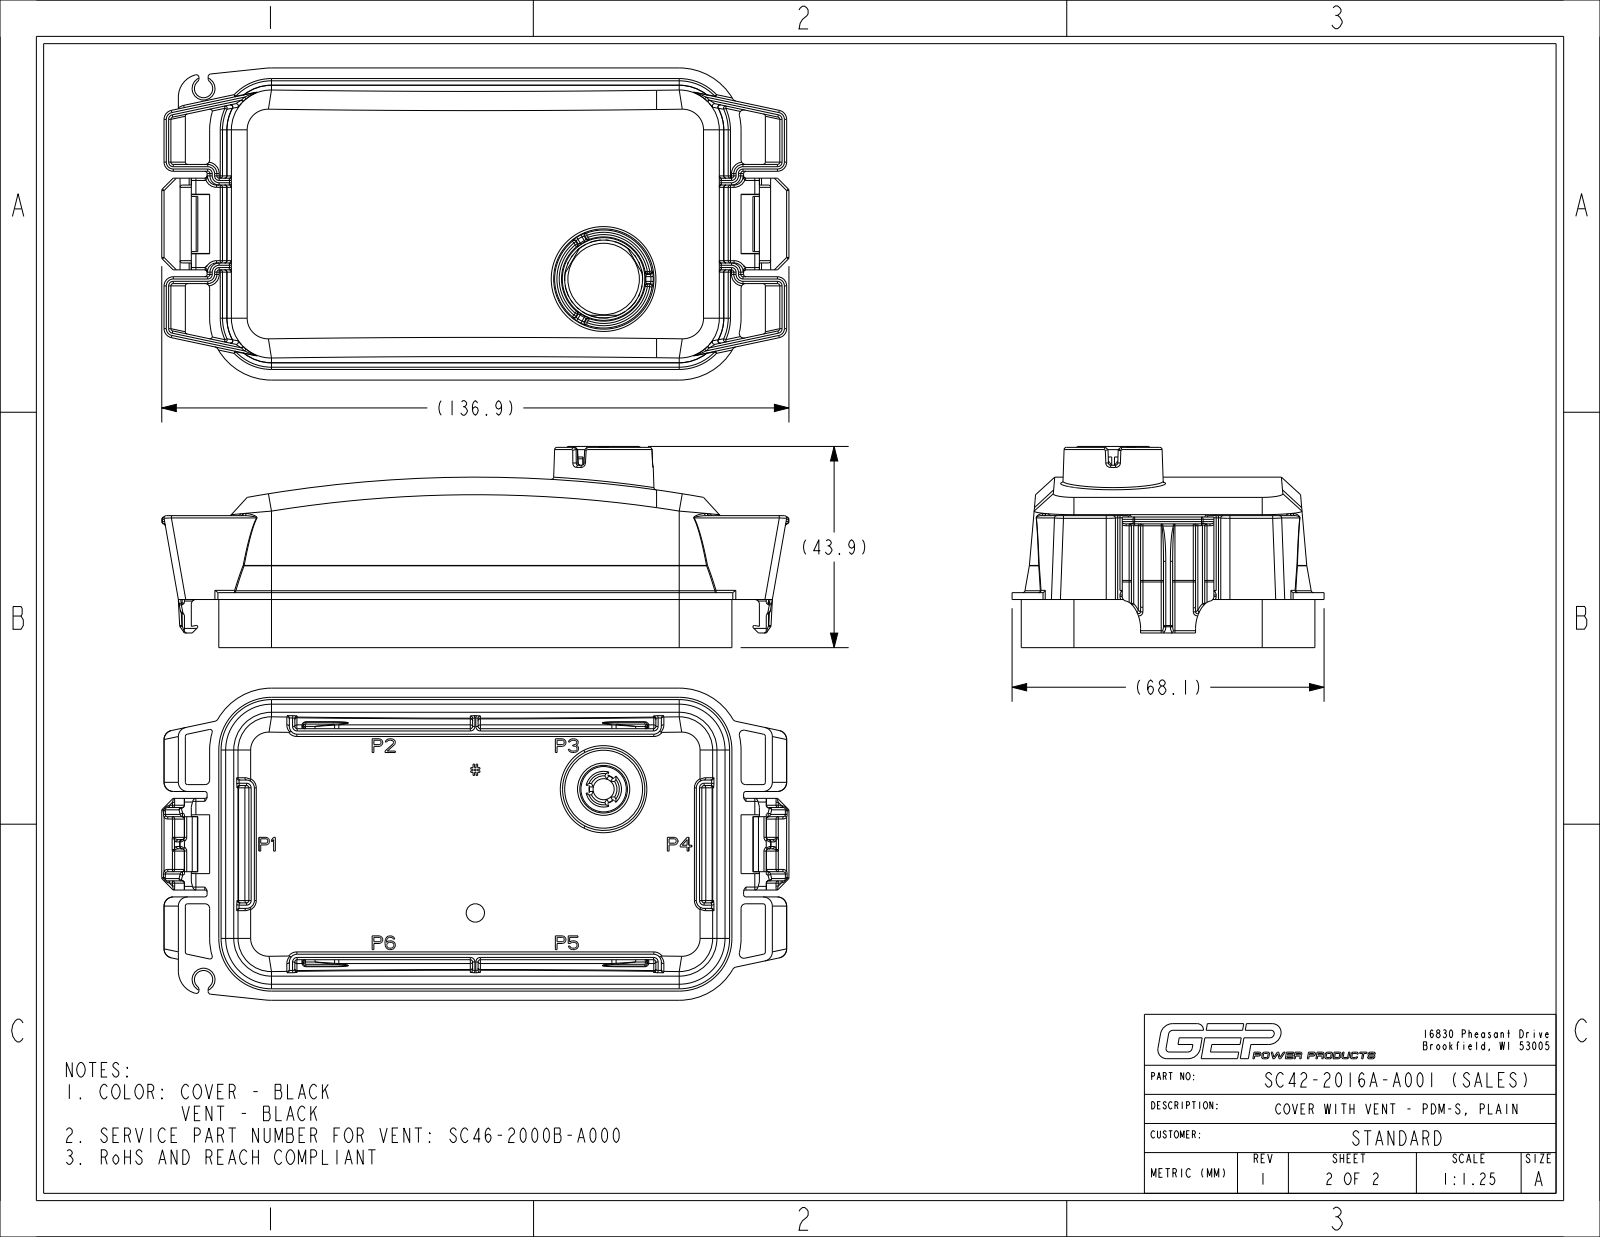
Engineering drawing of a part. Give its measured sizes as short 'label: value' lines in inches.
name: PC27-2000C-B001_NCF; PC46-2000B-A000_NCF; PC42-2016A-A001_NCF_ASM; SC42-2016A-A001_NCF_ASM
written by: CREO PARAMETRIC BY PTC INC, 2017110 (CONFIG_CONTROL_DESIGN)
unit: in
bodies: 3 solids, 1685 faces (467 planar, 452 cylindrical, 766 other)
size: 5.39 × 2.681 × 1.728
volume: 2.198 in³; area: 74.41 in²
holes: 1× ⌀0.157, 1× ⌀0.181, 1× ⌀0.252, 1× ⌀0.378
bosses: 1× ⌀0.669, 1× ⌀0.409, 1× ⌀0.244
rounds: 234× R0.02, 22× R0.079, 19× R0.039, 8× R0.067, 4× R0.016, 4× R0.02, 4× R0.024, 4× R0.394
face distances: 0.059, 2.465, 0.317, 2.207, 0.258, 2.148, 0.047, 0.079, 2.524, 0.27
hole spacings: 3.807
